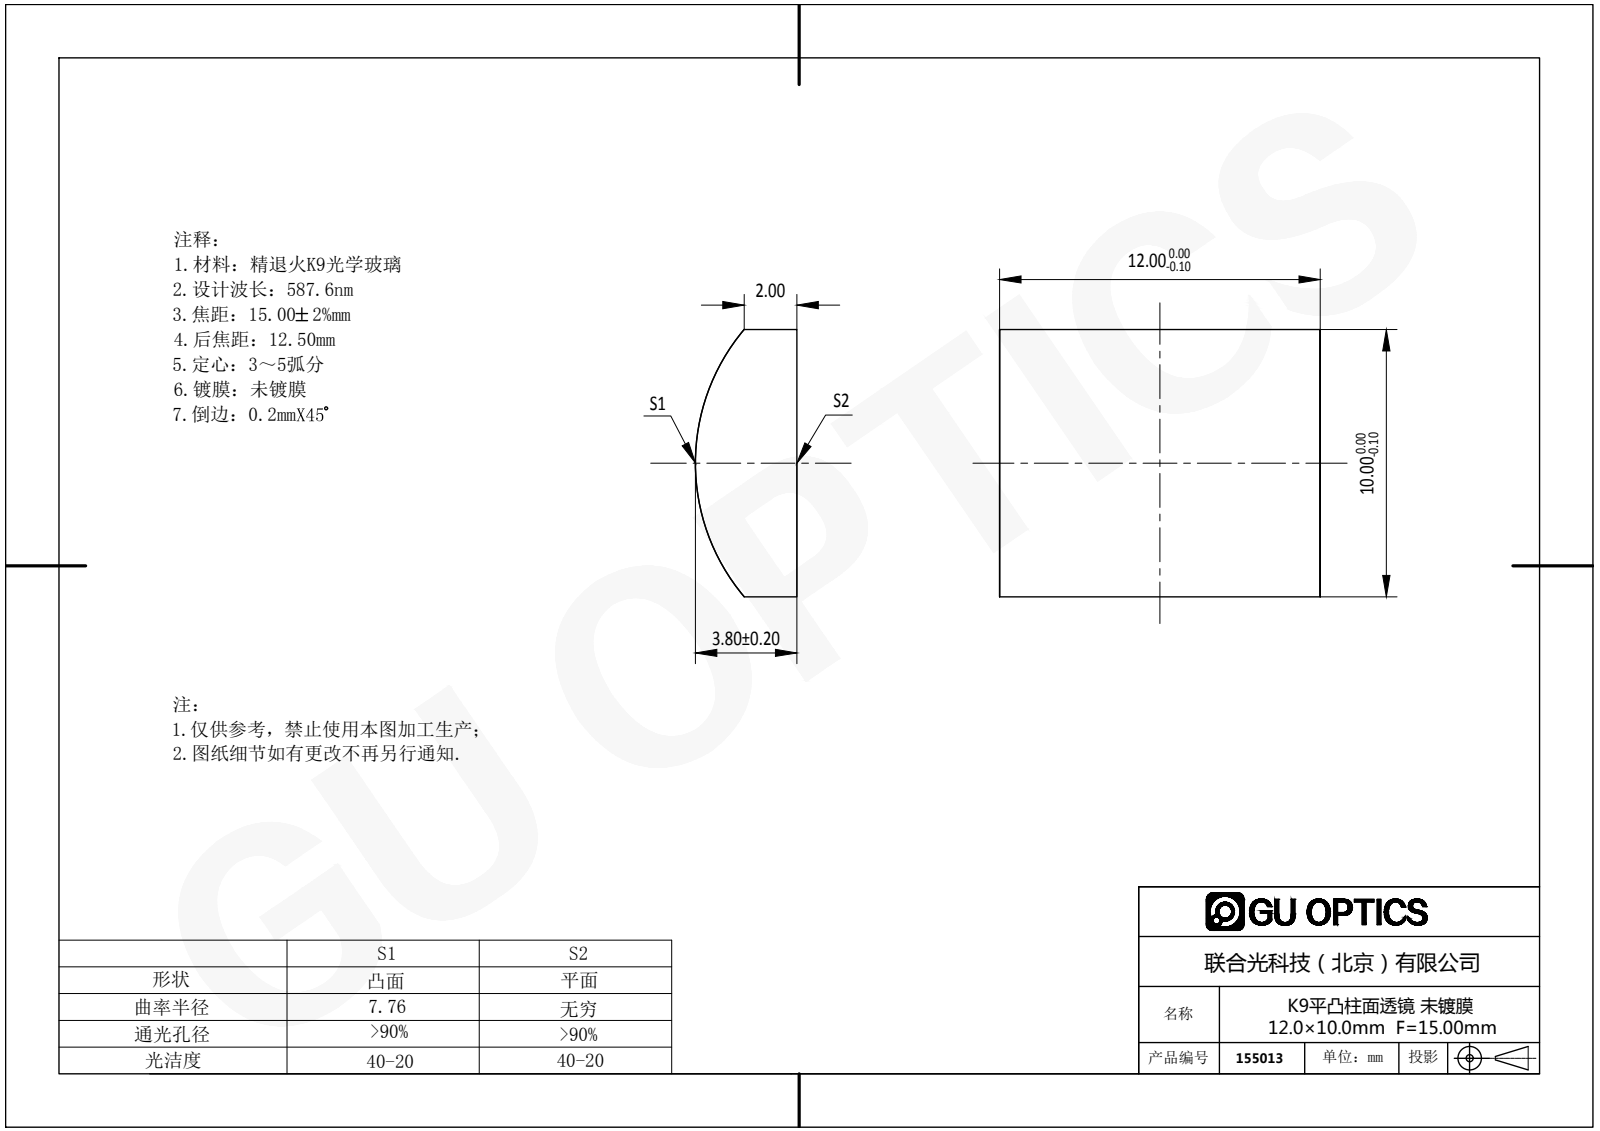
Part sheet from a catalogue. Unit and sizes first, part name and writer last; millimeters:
Units: millimetres
Overall size (bounding box): 12 × 10 × 3.8
Partial cylindrical surfaces — rounded edges, fillets, slot ends (radius × count): R7.76 ×1
Main face-to-face distances: 12, 10
Volume: 387 mm³ · Surface area: 362 mm²
Bodies: 1 solid, 6 faces (5 planar, 1 cylindrical, 0 other)
Part name (STEP PRODUCT): 155013
STEP written by: SolidWorks 2016 (AUTOMOTIVE_DESIGN)
